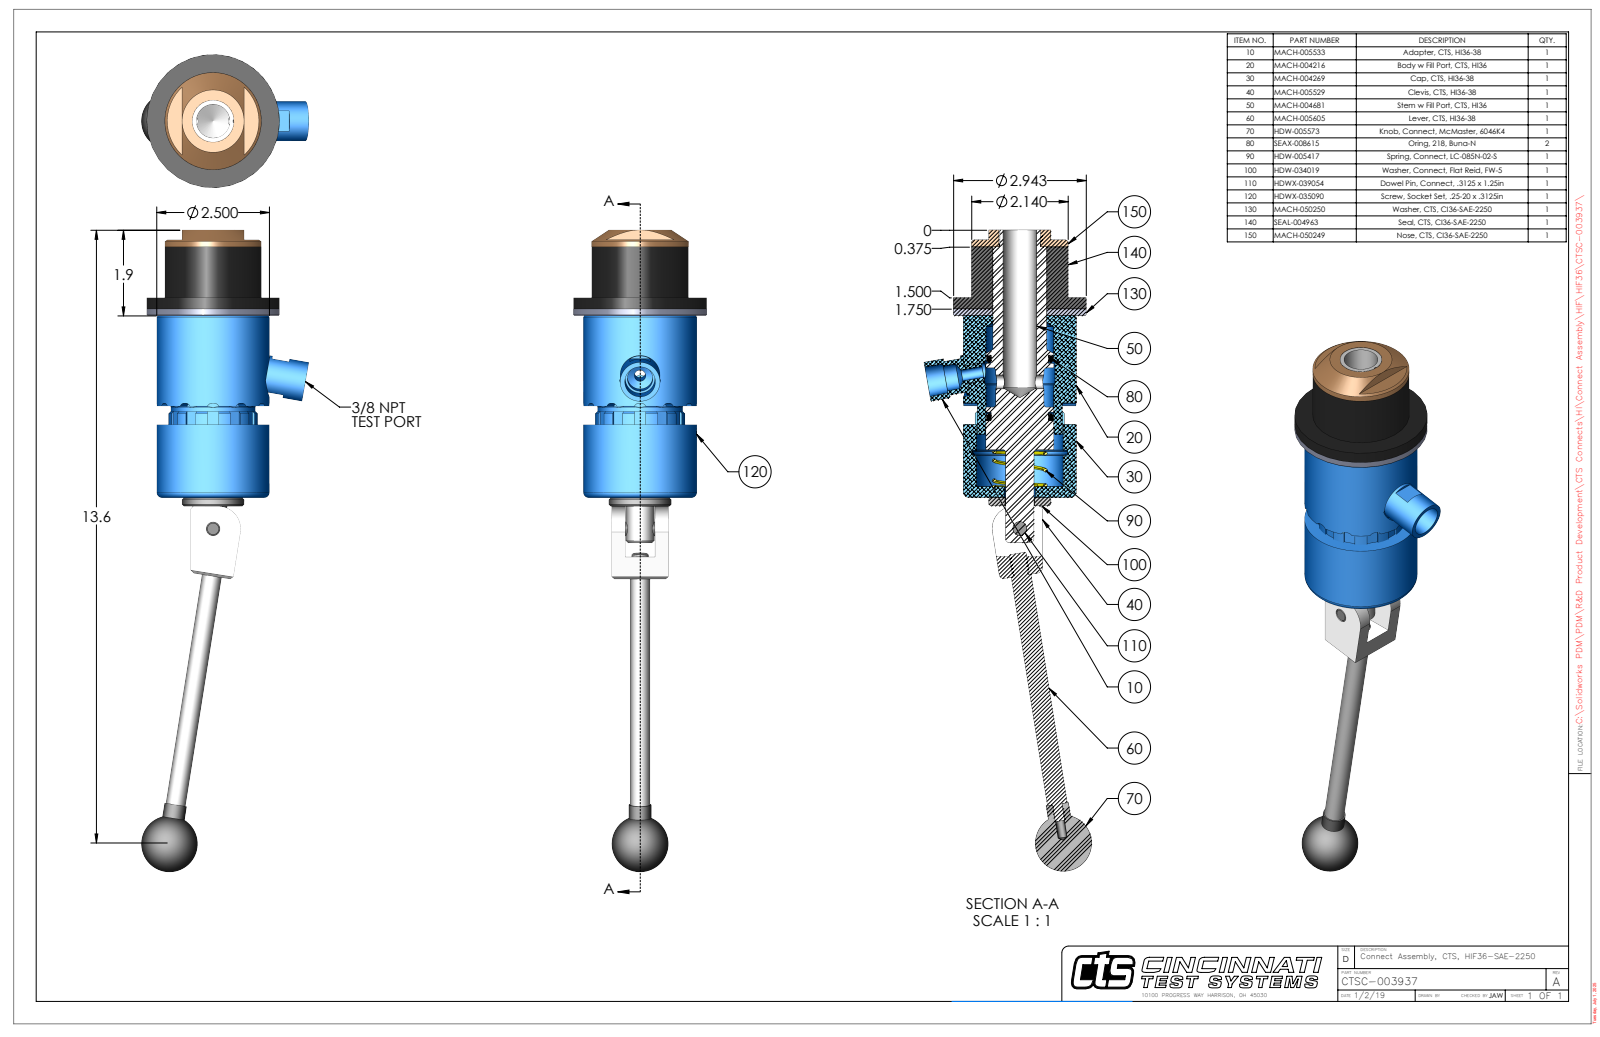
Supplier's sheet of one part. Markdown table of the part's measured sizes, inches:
| quantity | value |
| --- | --- |
| part name | CTSC-003937 |
| STEP written by | SolidWorks 2023 (AUTOMOTIVE_DESIGN) |
| units | inches |
| bodies | 11 solids, 401 faces (171 planar, 147 cylindrical, 83 other) |
| overall size | 14.215 × 3.716 × 2.943 |
| volume | 29.01 in³ |
| surface area | 147.7 in² |
| round holes (diameter × count) | 0.201 × 2, 0.15 × 1, 0.25 × 1, 0.311 × 1, 0.312 × 1, 0.313 × 1, 0.314 × 1, 0.391 × 1, 0.562 × 1, 0.656 × 1, 0.696 × 1, 0.75 × 1 |
| round bosses / shafts (diameter × count) | 2.943 × 1, 2.5 × 1, 2.14 × 1, 1.875 × 1, 1.38 × 1, 1.186 × 1, 1 × 1, 0.904 × 1 |
| partial cylindrical surfaces (radius × count) | 0.12 × 12, 0.029 × 2, 0.433 × 1, 0.47 × 1, 0.5 × 1, 0.961 × 1, 0.996 × 1, 1.162 × 1 |
| main face-to-face distances | 0.15, 1.375, 1.525, 4.03, 4.18, 5.555, 0.25, 1.125, 4.43, 0.4 |
| hole center spacings | 0.74, 2.118, 2.858 |
